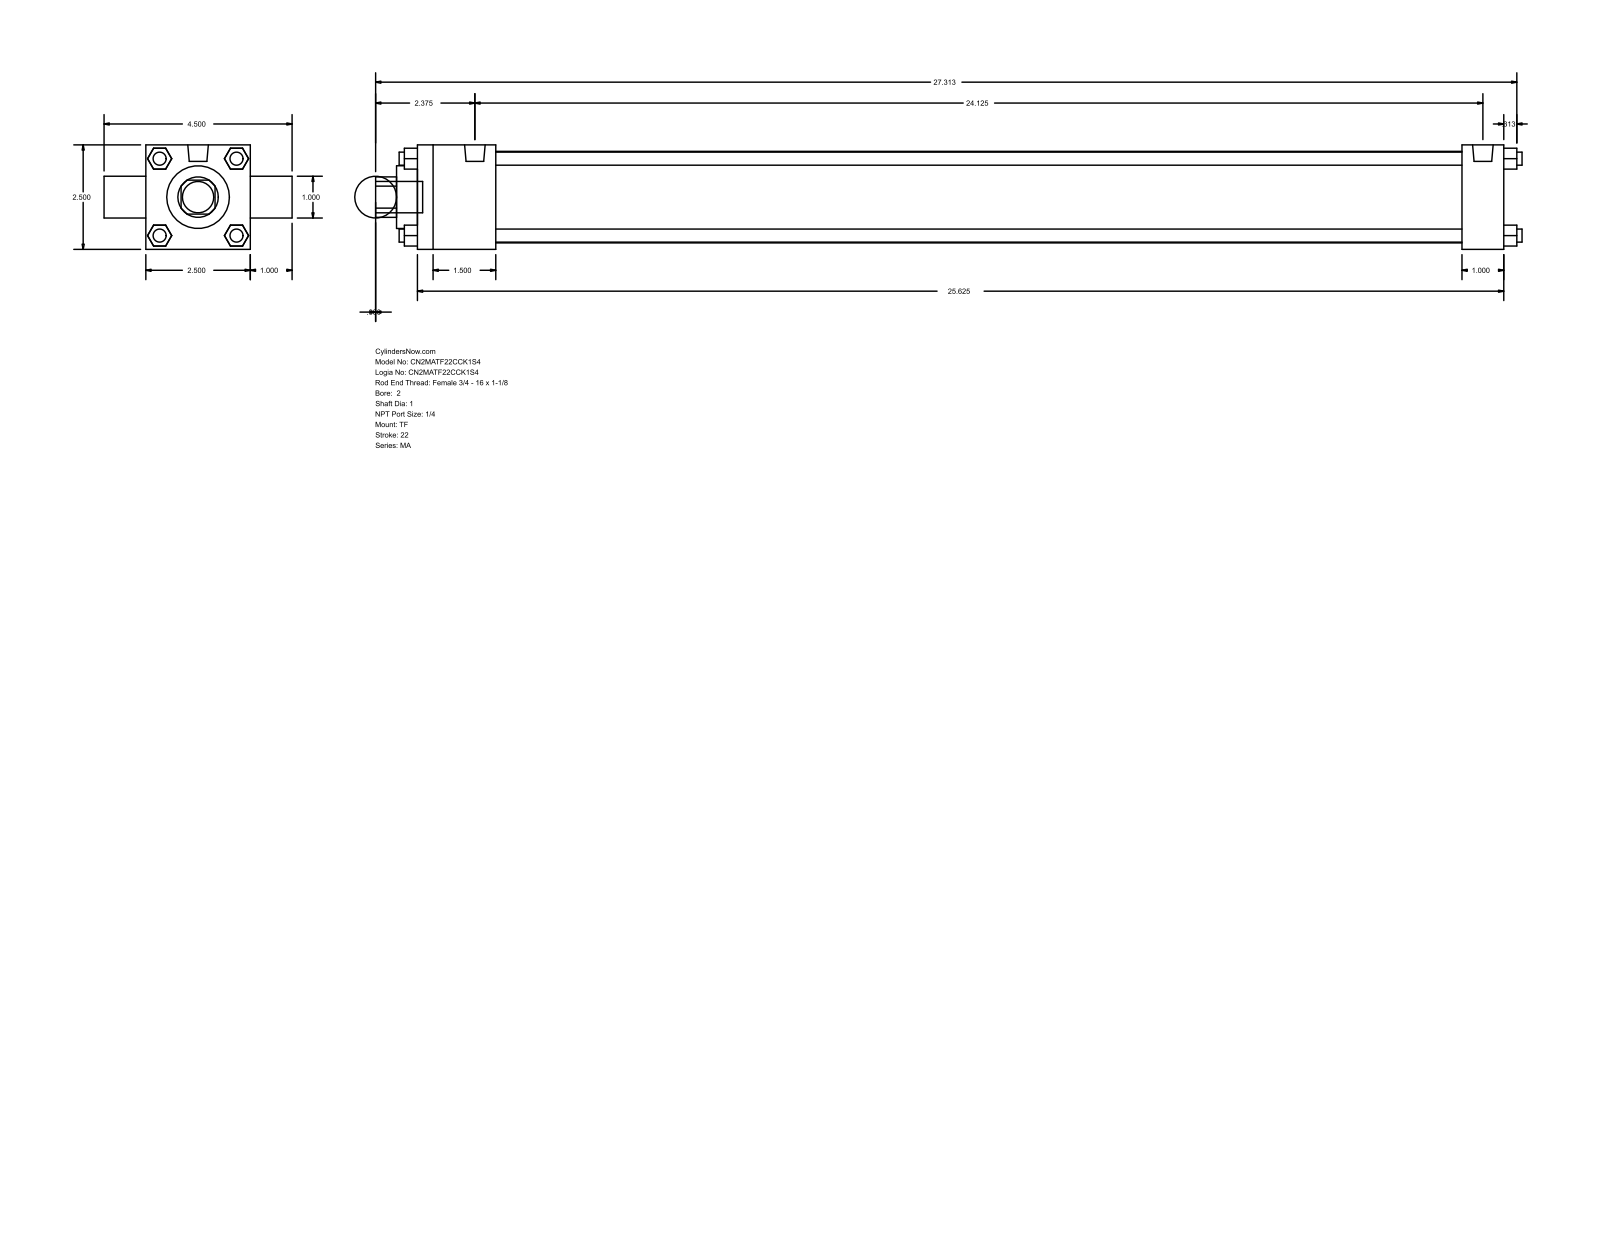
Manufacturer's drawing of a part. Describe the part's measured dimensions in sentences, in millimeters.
The part is named "MA_TF__0200_1". Its 3-D file was written by "GSSL Pune (CONFIG_CONTROL_DESIGN)". It is 0 solids with 120 faces: 92 planar, 28 cylindrical and 0 other. Overall it measures 696.91 by 114.3 by 63.5 millimeters. Round holes: 2 of diameter 25.4, 1 of diameter 38.1, 1 of diameter 55.63. Round bosses or shafts: 7 of diameter 7.94, 2 of diameter 12.49, 1 of diameter 19.05. Partial cylindrical surfaces (rounded edges, fillets, slot ends): 1 of radius 12.29. The main face-to-face distances are 63.5, 25.4, 660.4, 12.7, 47.63, 635, 587.37, 612.77, 88.9, 40.47.
